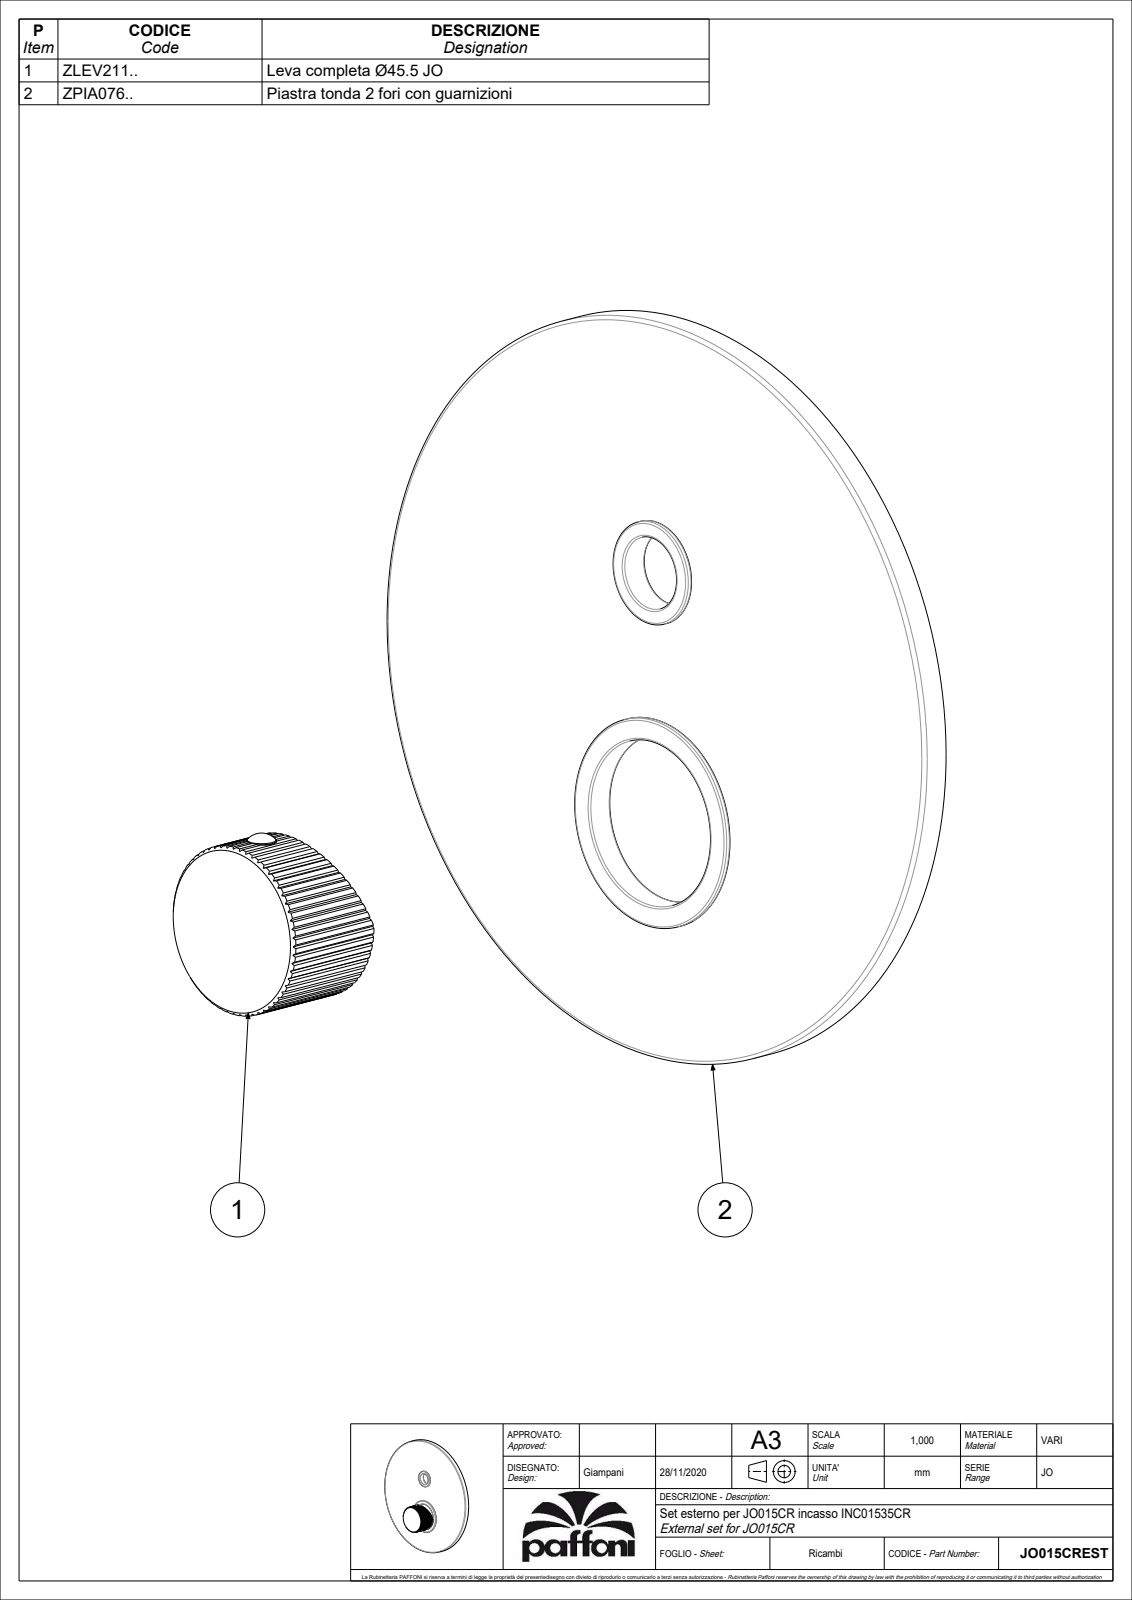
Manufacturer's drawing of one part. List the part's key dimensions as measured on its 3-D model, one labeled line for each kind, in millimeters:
Part name (STEP PRODUCT): JO015CREST
STEP written by: CREO PARAMETRIC BY PTC INC, 2020044 (CONFIG_CONTROL_DESIGN)
Units: millimetres
Bodies: 2 solids, 387 faces (203 planar, 129 cylindrical, 55 other)
Overall size (bounding box): 200 × 200 × 41.4
Volume: 157 423 mm³ · Surface area: 92 213 mm²
Round holes (diameter × count): ⌀3 ×1, ⌀10.5 ×1, ⌀19.1 ×1, ⌀42 ×1, ⌀44.6 ×1, ⌀50 ×1, ⌀145 ×1, ⌀198 ×1
Round bosses / shafts (diameter × count): ⌀200 ×1, ⌀195 ×1, ⌀56.2 ×1, ⌀49.9 ×1, ⌀25.1 ×1, ⌀23.5 ×1, ⌀16 ×1, ⌀7.6 ×1
Partial cylindrical surfaces — rounded edges, fillets, slot ends (radius × count): R4 ×1, R22.75 ×1
Main face-to-face distances: 1, 8, 9, 30, 29, 38, 2, 3, 11, 27
Hole centre spacings: 32.2, 35.8, 68
